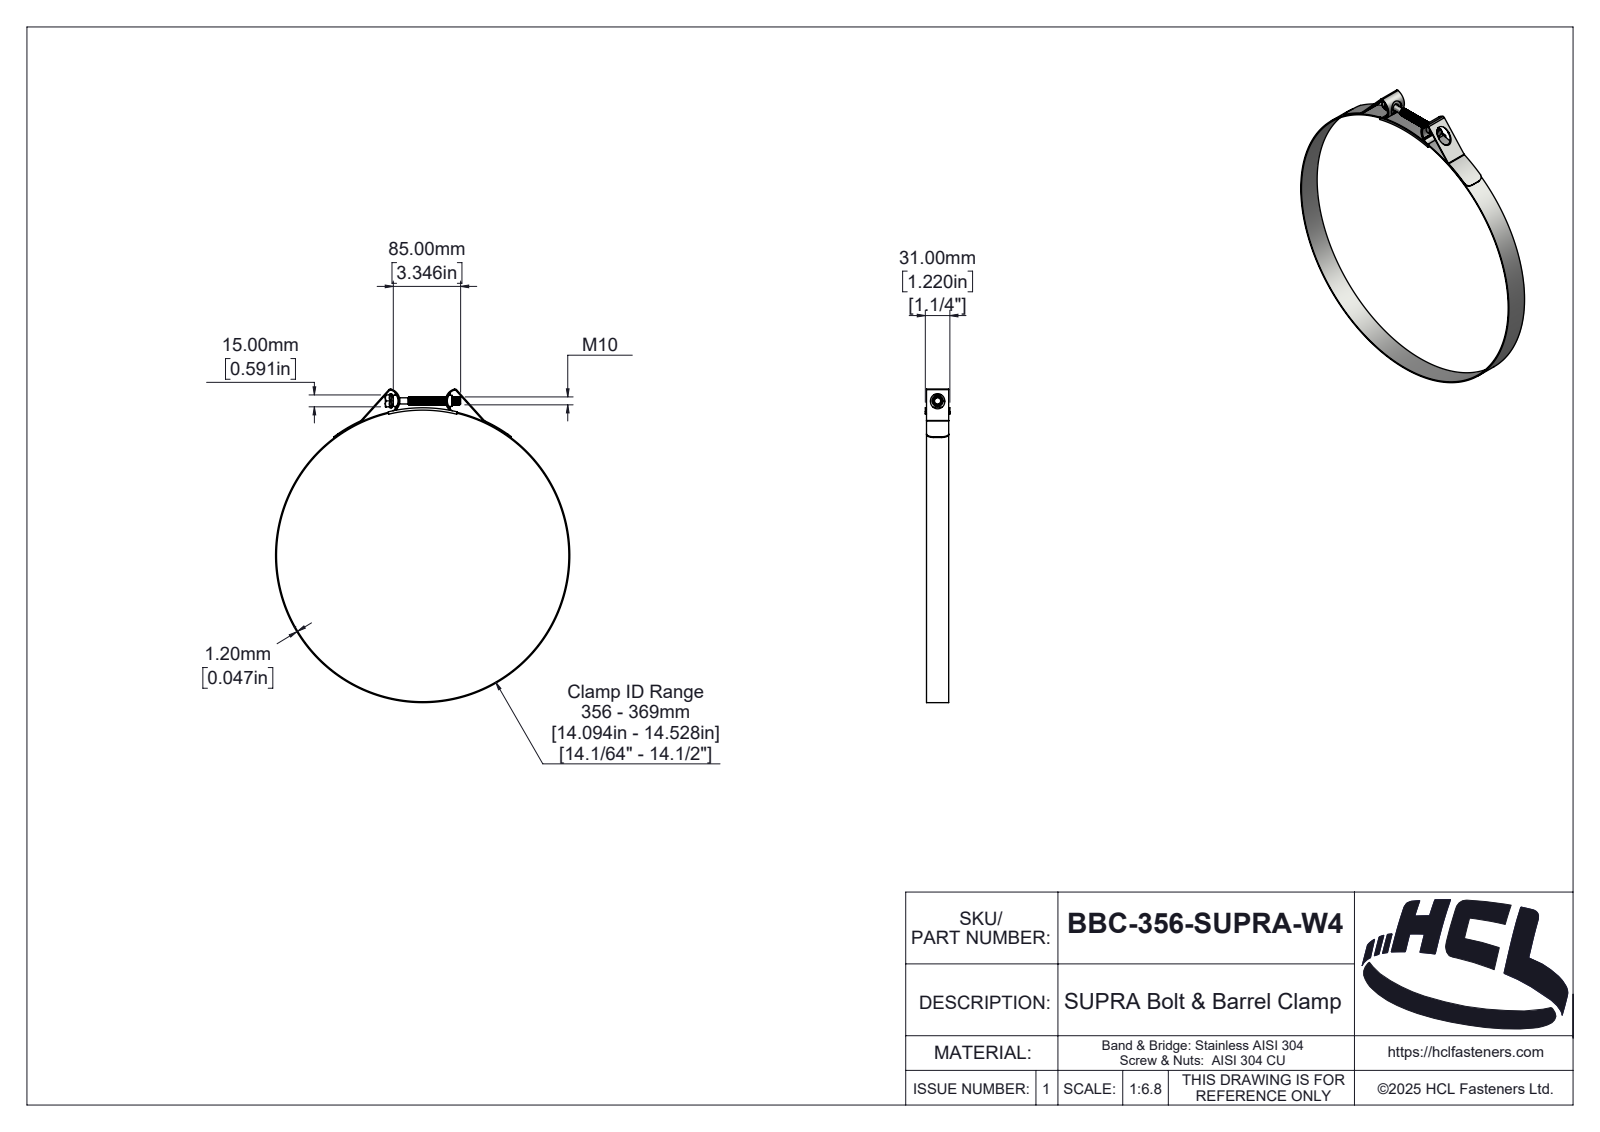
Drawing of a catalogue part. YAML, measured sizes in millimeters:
part_name: "BBC-356-SUPRA-W4"
step_written_by: "SolidWorks 2025 (AUTOMOTIVE_DESIGN)"
units: millimeters
bodies: {solids: 5, faces: 378, planar: 50, cylindrical: 242, other: 86}
overall_size: [395.65, 371.4, 31]
volume: 56686
surface_area: 90449
round_holes:
  - {diameter: 369, count: 1}
round_bosses_or_shafts:
  - {diameter: 371.4, count: 1}
  - {diameter: 17.32, count: 1}
  - {diameter: 14, count: 1}
  - {diameter: 10, count: 1}
  - {diameter: 7.8, count: 1}
partial_cylinders:
  - {radius: 1, count: 4}
  - {radius: 1.3, count: 2}
  - {radius: 2, count: 2}
  - {radius: 2.5, count: 2}
  - {radius: 3.2, count: 2}
  - {radius: 9, count: 2}
  - {radius: 13.13, count: 2}
  - {radius: 14.13, count: 2}
face_to_face_distances: [1.2, 28, 1.5, 29.5, 29.8, 28.3, 31, 28.6, 15, 12.5]
